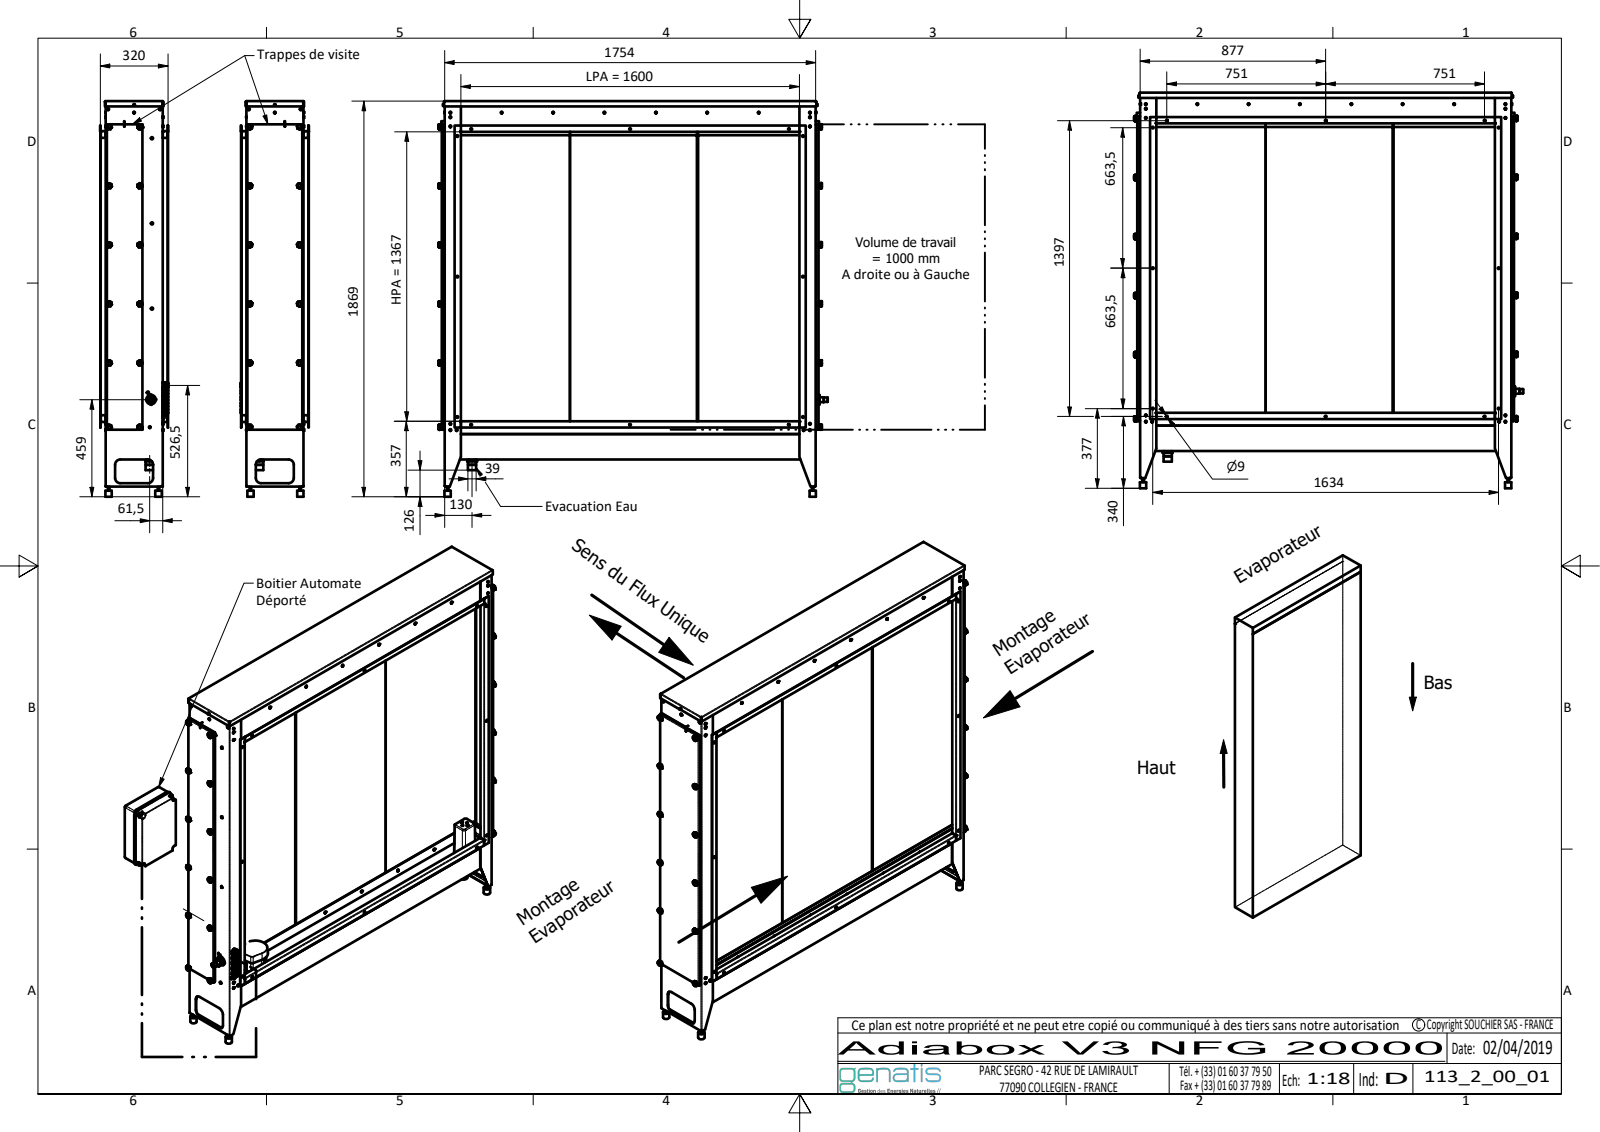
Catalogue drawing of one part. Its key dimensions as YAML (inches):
part_name: "113_2_00_01_-_Adiabox_V3; 113_2_00_06_-_Glissiere basse assemblee; 113_3_00_11_-_Cote gauche glissiere; 113_3_00_15_-_Tole de fond pliee (+8 more)"
step_written_by: "Autodesk Inventor 2022 (AUTOMOTIVE_DESIGN)"
units: inches
bodies: {solids: 260, faces: 6654, planar: 3019, cylindrical: 2300, other: 1335}
overall_size: [73.583, 72.461, 12.736]
volume: 26233
surface_area: 39779
round_holes:
  - {diameter: 0.165, count: 67}
  - {diameter: 0.118, count: 61}
  - {diameter: 0.236, count: 46}
  - {diameter: 0.163, count: 38}
  - {diameter: 0.276, count: 22}
  - {diameter: 0.354, count: 15}
  - {diameter: 0.205, count: 12}
  - {diameter: 0.63, count: 11}
  - {diameter: 0.551, count: 8}
  - {diameter: 0.295, count: 6}
  - {diameter: 0.787, count: 6}
  - {diameter: 0.256, count: 5}
round_bosses_or_shafts:
  - {diameter: 0.311, count: 59}
  - {diameter: 0.157, count: 59}
  - {diameter: 0.433, count: 42}
  - {diameter: 0.197, count: 42}
  - {diameter: 0.276, count: 30}
  - {diameter: 0.906, count: 10}
  - {diameter: 0.335, count: 10}
  - {diameter: 0.374, count: 6}
partial_cylinders:
  - {radius: 0.118, count: 264}
  - {radius: 0.315, count: 168}
  - {radius: 0.059, count: 92}
  - {radius: 0.492, count: 24}
  - {radius: 0.039, count: 22}
  - {radius: 0.197, count: 16}
  - {radius: 0.079, count: 15}
  - {radius: 0.394, count: 10}
face_to_face_distances: [0.059, 3.937, 0.079, 69.528, 0.531, 66.555, 10.433, 10.492, 0.02, 0.118]
hole_center_spacings: [9.561, 19.122, 28.684, 38.245, 59.28, 61.55, 9.608, 65.157]
